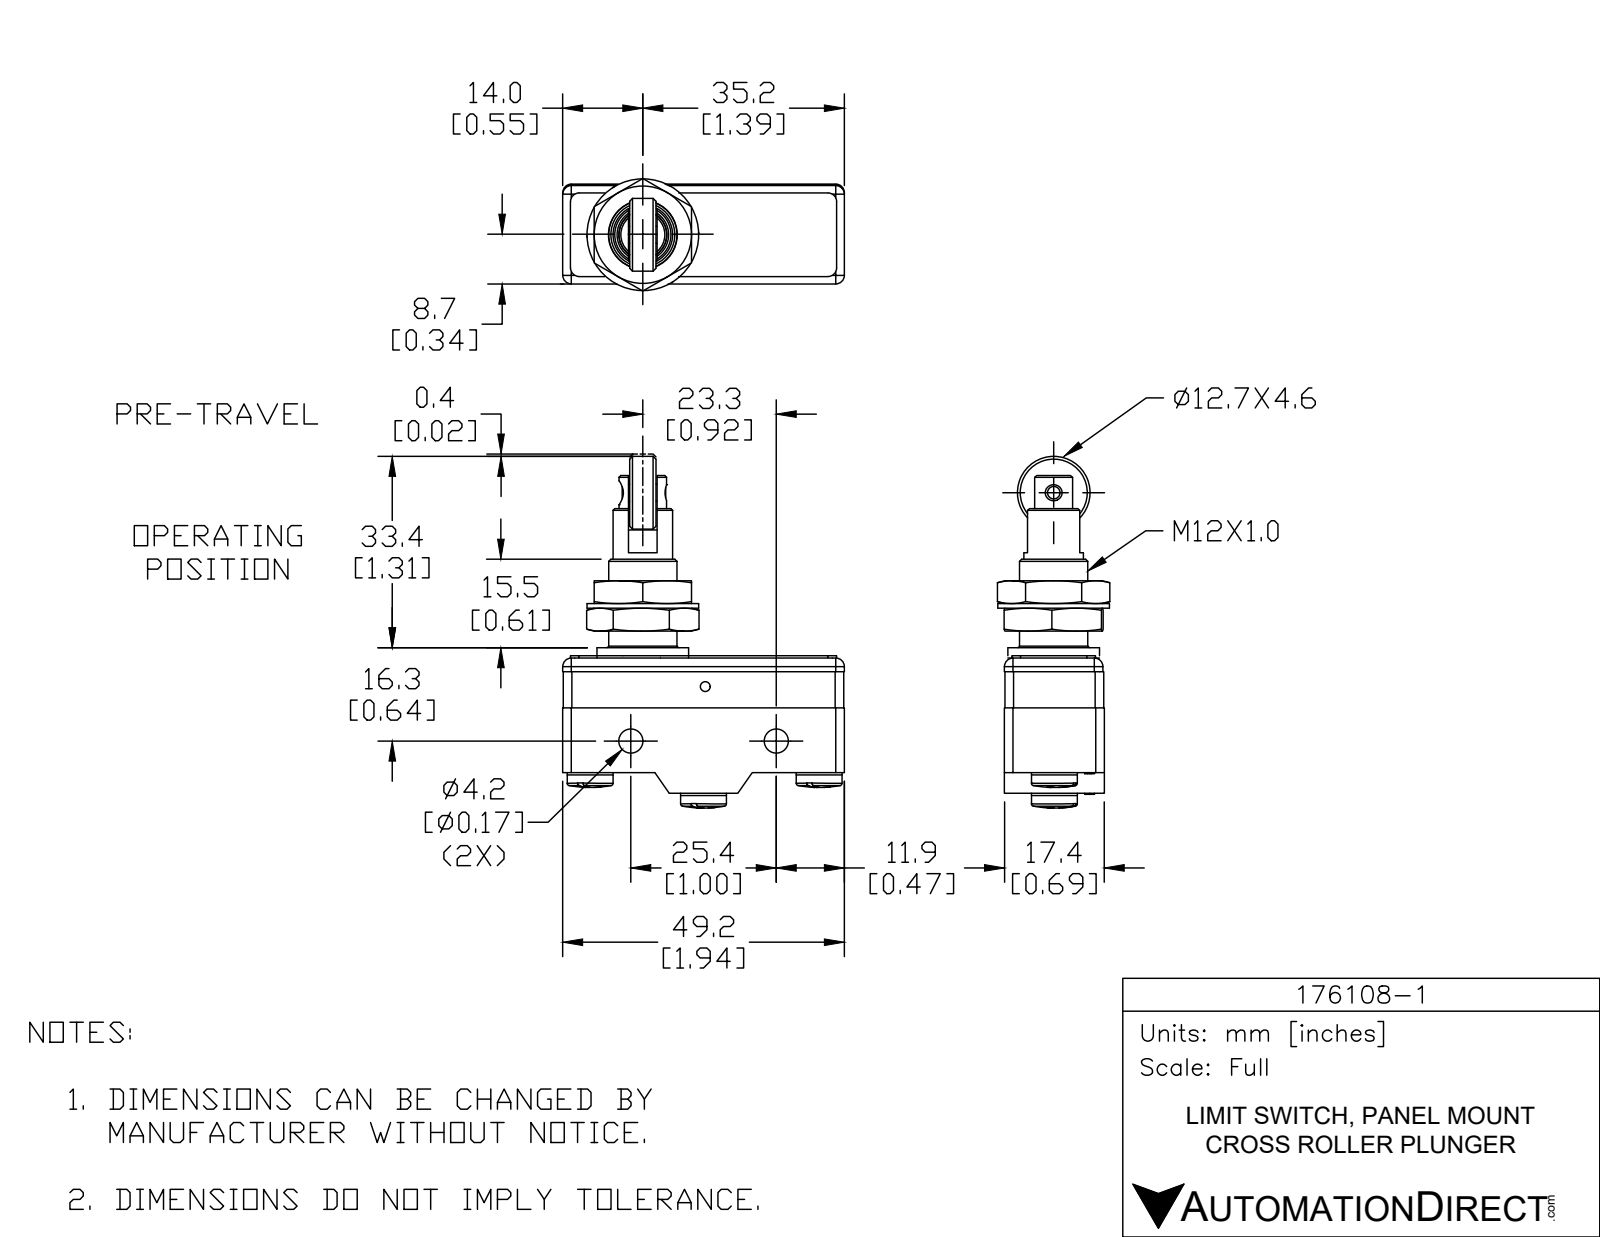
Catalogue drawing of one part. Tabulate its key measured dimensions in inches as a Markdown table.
| quantity | value |
| --- | --- |
| part name | 176-MS (Screw Terminal)-Panel Mount Cross Roller Plunger |
| STEP written by | SolidWorks 2018 (AUTOMOTIVE_DESIGN) |
| units | inches |
| bodies | 15 solids, 605 faces (263 planar, 144 cylindrical, 198 other) |
| overall size | 2.442 × 1.937 × 0.773 |
| volume | 1.368 in³ |
| surface area | 19.81 in² |
| round holes (diameter × count) | 0.15 × 3, 0.236 × 3, 0.165 × 2, 0.43 × 2, 0.067 × 1, 0.079 × 1, 0.126 × 1, 0.161 × 1, 0.295 × 1, 0.331 × 1 |
| round bosses / shafts (diameter × count) | 0.315 × 3, 0.768 × 1, 0.63 × 1, 0.626 × 1, 0.5 × 1, 0.47 × 1, 0.409 × 1, 0.327 × 1 |
| partial cylindrical surfaces (radius × count) | 0.059 × 18, 0.012 × 12, 0.116 × 3, 0.25 × 1, 0.317 × 1 |
| main face-to-face distances | 0.693, 0.683, 0.687, 0.803, 0.11, 0.189, 1.143, 0.016, 0.157, 0.679 |
| hole center spacings | 0.354, 0.425, 0.78, 0.795, 1.22, 1.575, 0.615, 0.634 |
